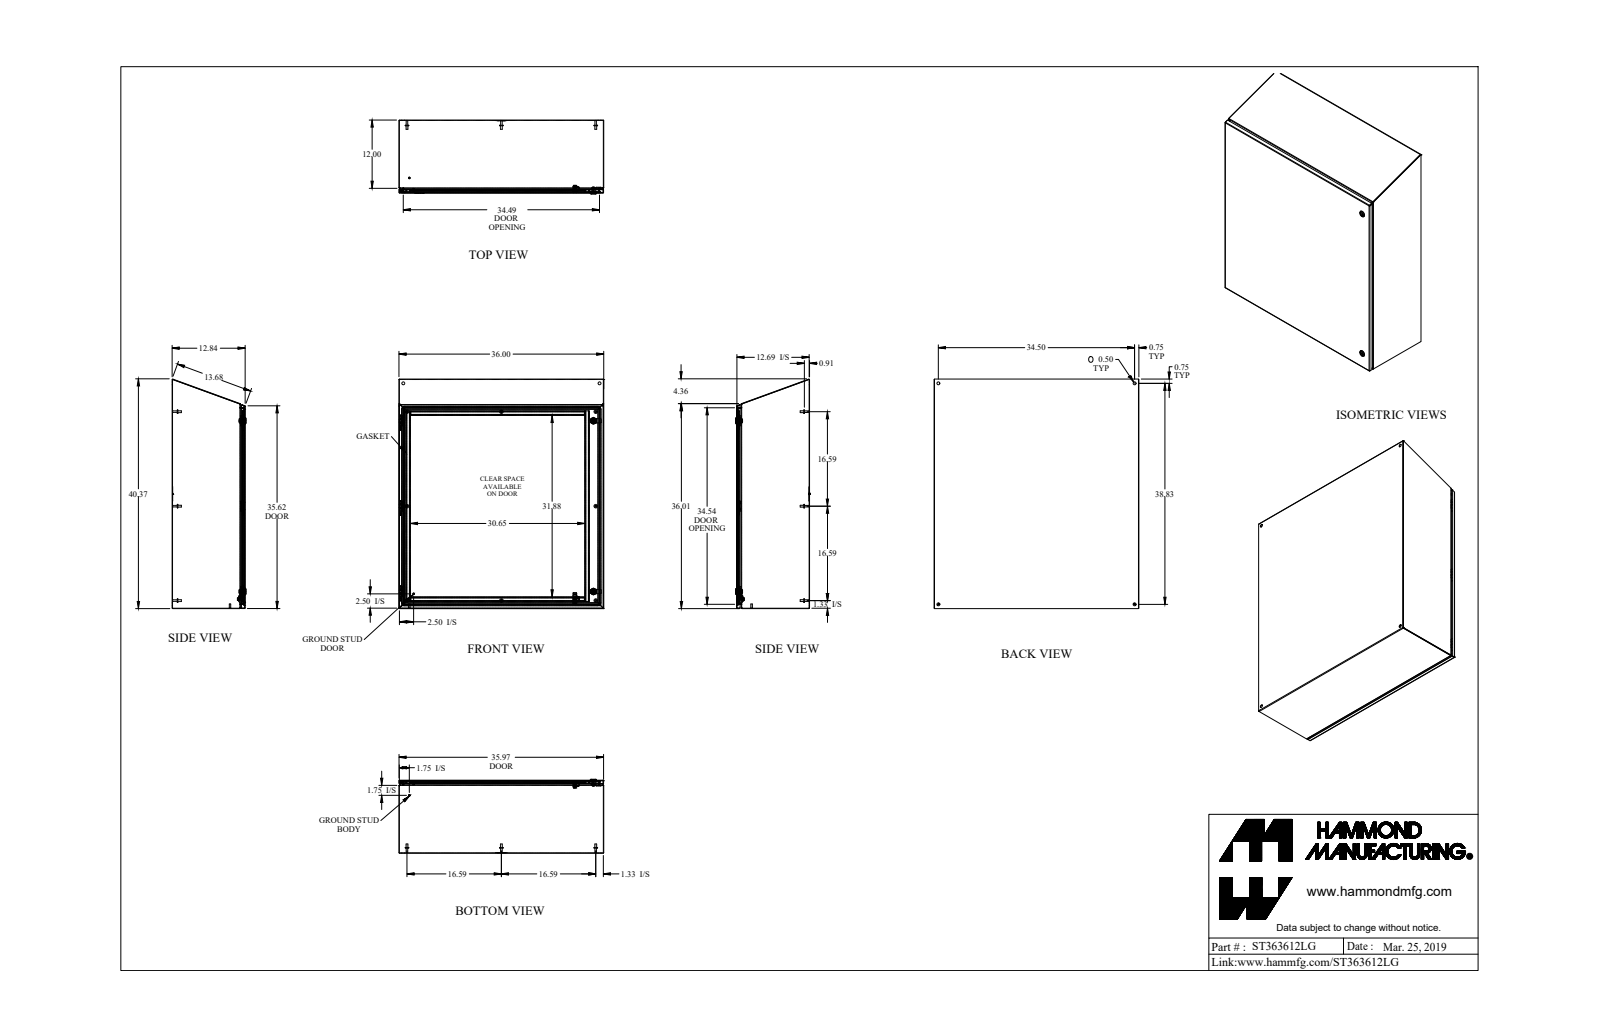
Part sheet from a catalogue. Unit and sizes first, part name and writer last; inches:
Units: inches
Overall size (bounding box): 40.328 × 36 × 12.997
Round holes (diameter × count): ⌀0.5 ×4, ⌀0.172 ×2, ⌀0.232 ×2, ⌀0.242 ×2, ⌀0.625 ×2, ⌀0.785 ×2, ⌀0.196 ×1, ⌀0.24 ×1, ⌀0.275 ×1, ⌀0.375 ×1
Round bosses / shafts (diameter × count): ⌀0.313 ×8, ⌀0.27 ×8, ⌀0.625 ×7, ⌀1.1 ×2, ⌀0.625 ×2, ⌀0.525 ×2, ⌀0.356 ×2, ⌀0.292 ×2
Partial cylindrical surfaces — rounded edges, fillets, slot ends (radius × count): R0.043 ×24, R0.081 ×24, R0.036 ×18, R0.108 ×18, R0.062 ×10, R0.094 ×10, R0.016 ×9, R0.063 ×9
Main face-to-face distances: 0.072, 12.765, 12.693, 12.837, 35.928, 35.856, 36, 0.837, 11.928, 0.038
Hole centre spacings: 34.5, 38.828, 51.941, 2.493, 3.538, 4.444, 6.664, 30
Volume: 370.9 in³ · Surface area: 10 476 in²
Bodies: 43 solids, 1176 faces (563 planar, 390 cylindrical, 223 other)
Part name (STEP PRODUCT): ST363612LG
STEP written by: SolidWorks 2018 (AUTOMOTIVE_DESIGN)
